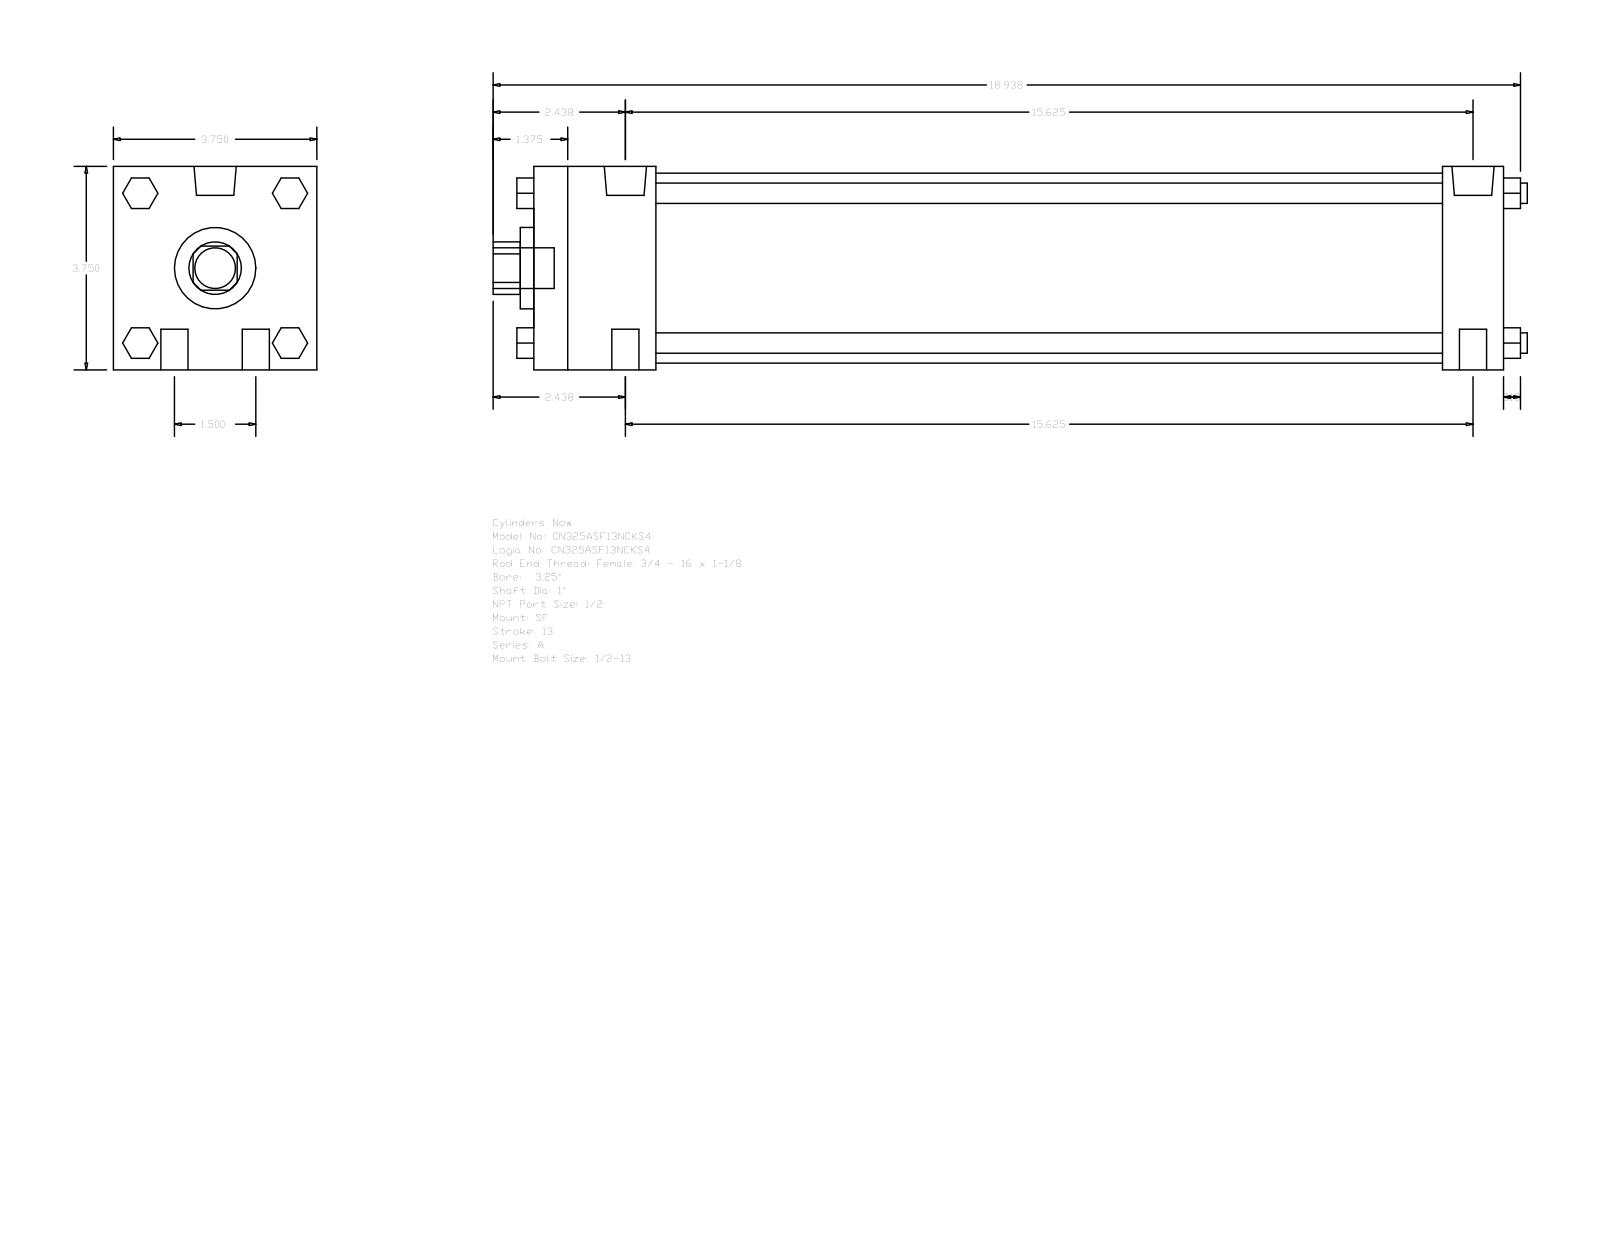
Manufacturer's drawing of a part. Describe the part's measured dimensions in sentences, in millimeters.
The part is named "A_SF__0325_1". Its 3-D file was written by "GSSL Pune (CONFIG_CONTROL_DESIGN)". It is 0 solids with 124 faces: 94 planar, 30 cylindrical and 0 other. Overall it measures 484.19 by 95.25 by 95.25 millimeters. Round holes: 1 of diameter 25.4, 1 of diameter 38.1, 1 of diameter 88.9. Round bosses or shafts: 4 of diameter 12.7, 4 of diameter 9.53, 2 of diameter 19.77, 2 of diameter 8.73, 1 of diameter 19.05. Partial cylindrical surfaces (rounded edges, fillets, slot ends): 1 of radius 12.29. The main face-to-face distances are 95.24, 454.02, 28.57, 425.45, 57.15, 368.3, 396.87, 14.28, 35.05, 60.71.
